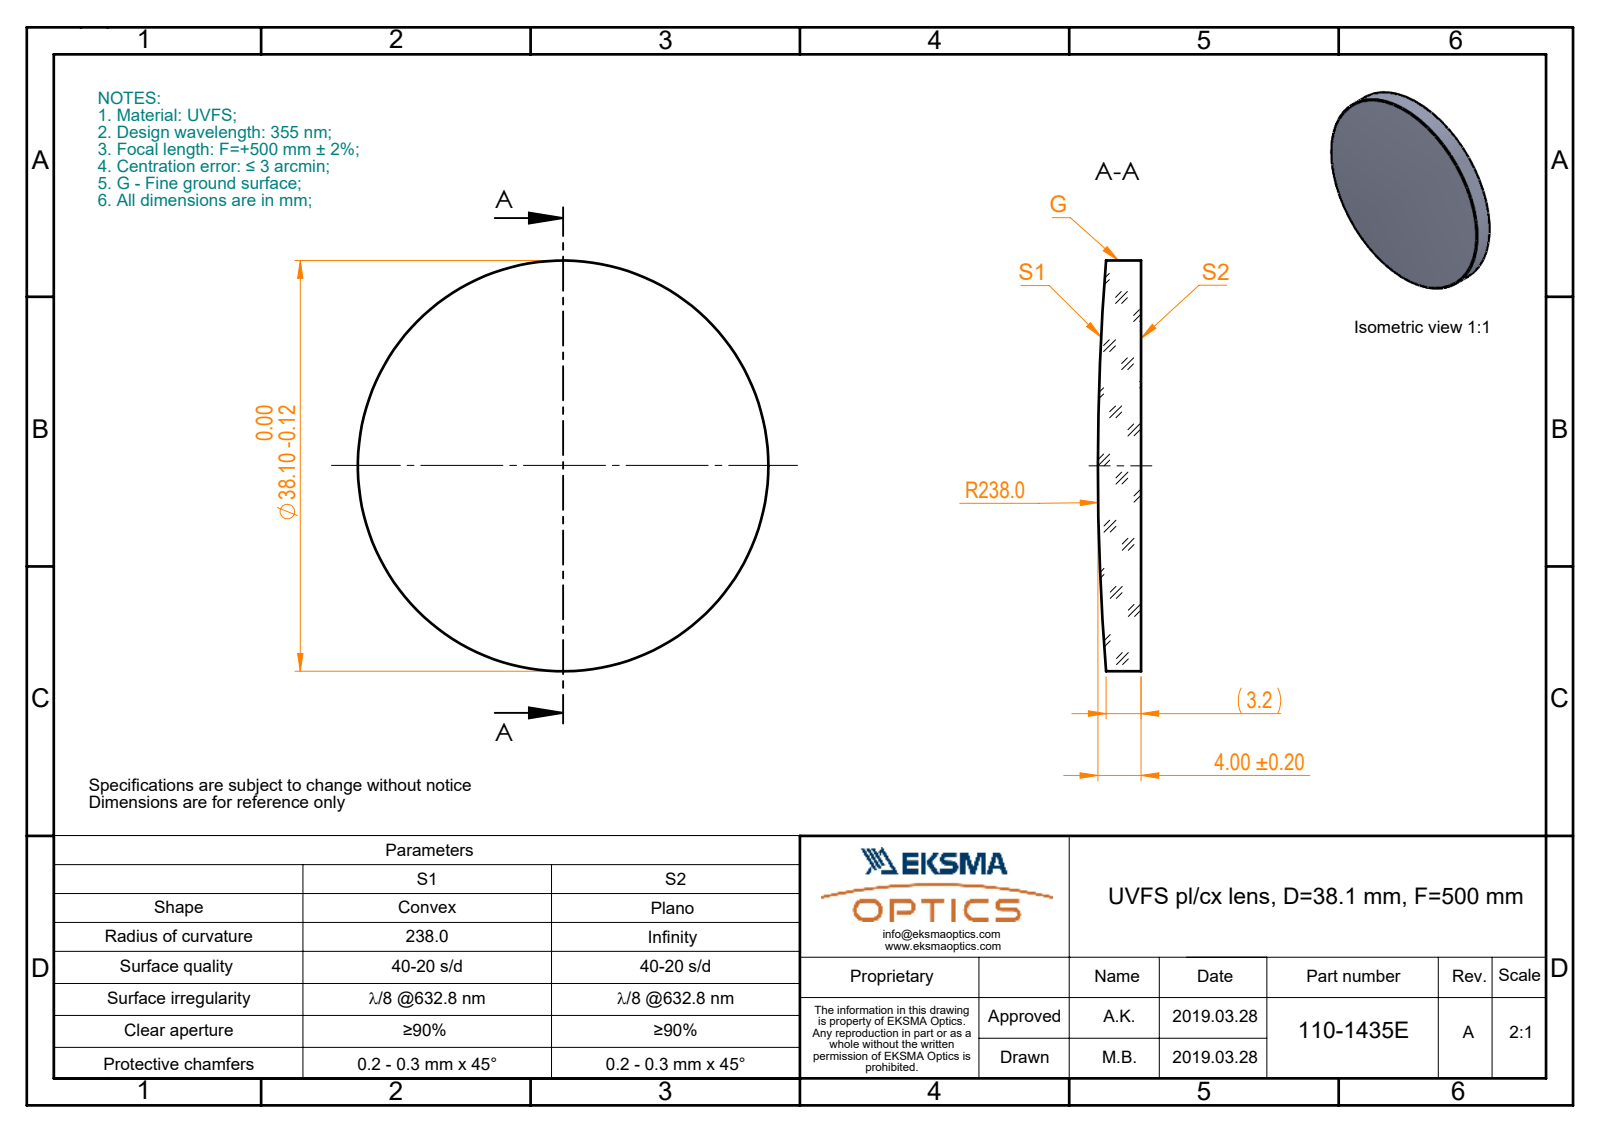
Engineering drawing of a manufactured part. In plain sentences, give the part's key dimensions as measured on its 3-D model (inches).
The part is named "110-1435E UVFS pl-cx 38.1 F500". Its 3-D file was written by "SolidWorks 2017 (CONFIG_CONTROL_DESIGN)". It is 1 solid with 5 faces: 1 planar, 2 cylindrical and 2 other. Overall it measures 1.5 by 1.5 by 0.157 inches. Its volume is 0.252 cubic inches and its surface area 4.137 square inches. Round bosses or shafts: 1 of diameter 1.5.
